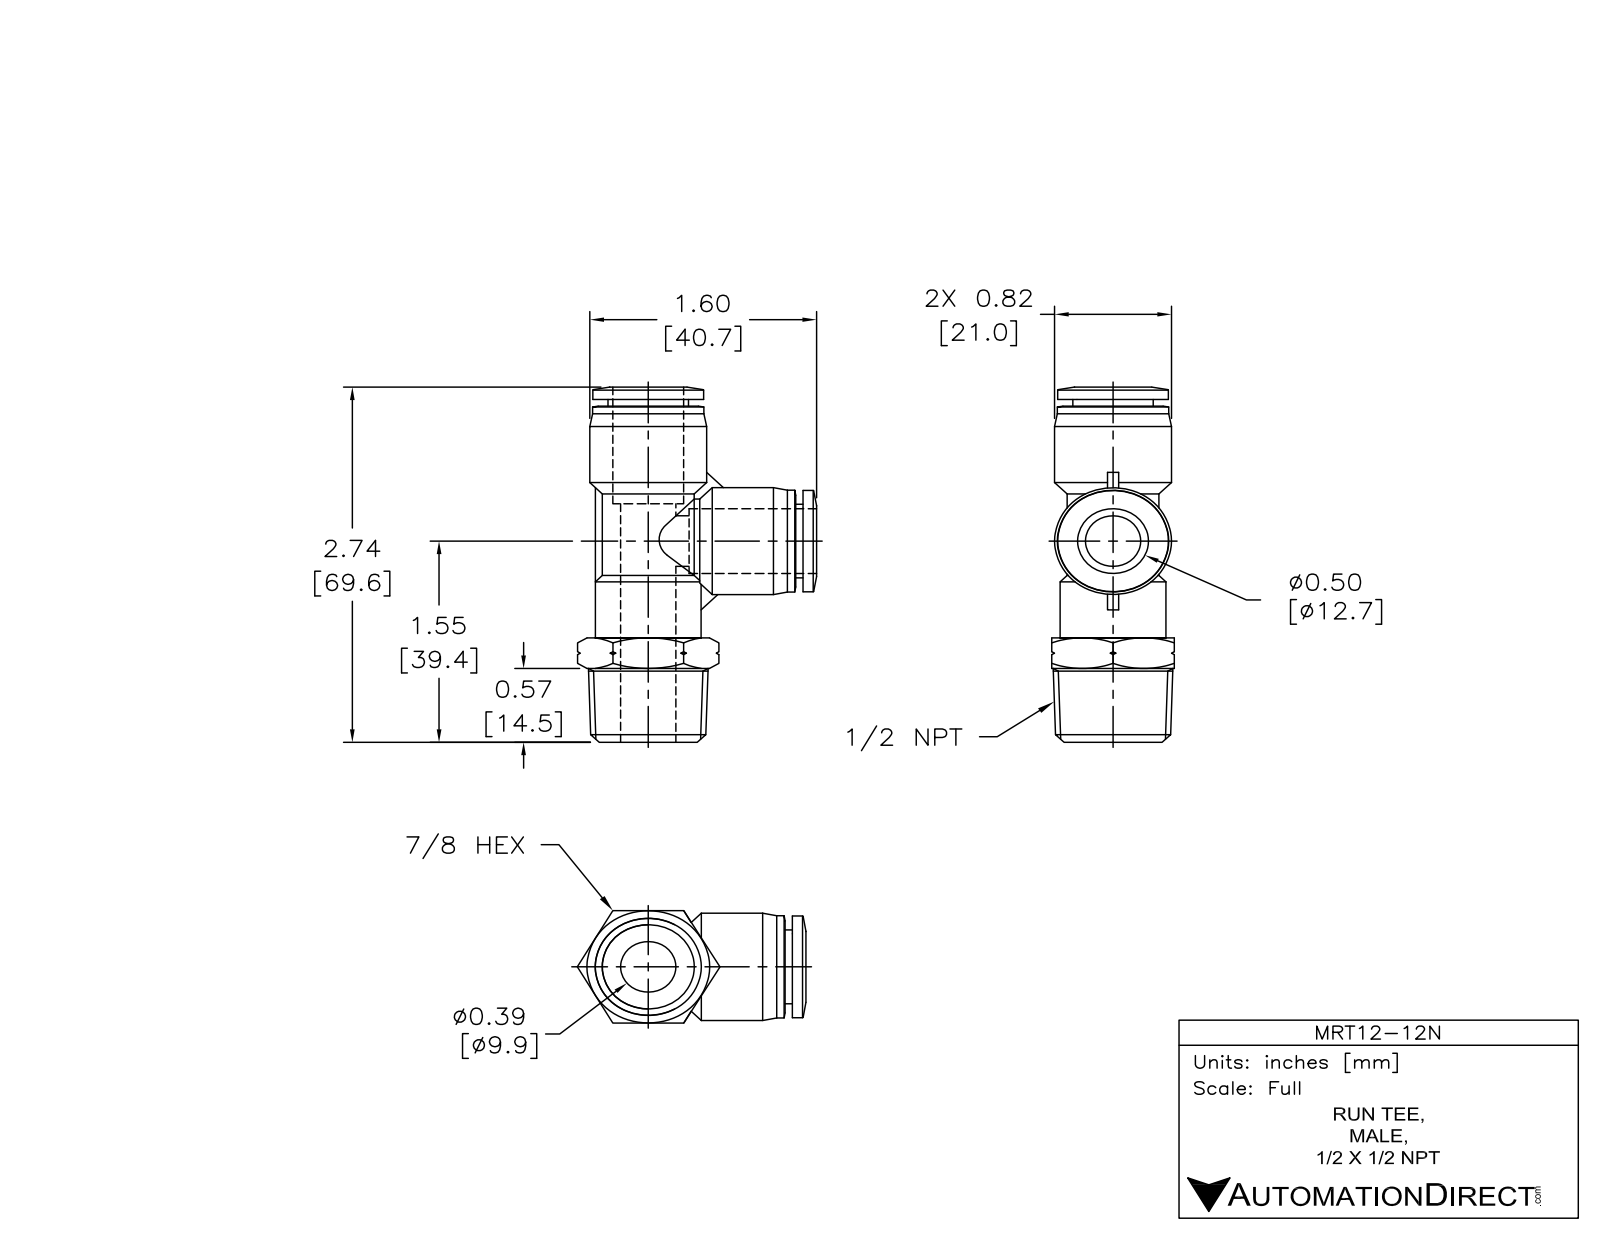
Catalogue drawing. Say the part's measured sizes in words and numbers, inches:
The part is named "MRT12-12N". Its 3-D file was written by "SolidWorks 2015 (AUTOMOTIVE_DESIGN)". It is 1 solid with 115 faces: 23 planar, 30 cylindrical and 62 other. Overall it measures 2.746 by 1.691 by 0.866 inches. Its volume is 1.11 cubic inches and its surface area 16.14 square inches. Round holes: 2 of diameter 0.394, 2 of diameter 0.51. Round bosses or shafts: 2 of diameter 0.827, 2 of diameter 0.787, 2 of diameter 0.783, 2 of diameter 0.65, 2 of diameter 0.569, 1 of diameter 0.748. The main face-to-face distances are 0.866, 0.051, 2.65, 0.762, 0.813, 0.807, 1.843, 2.598, 1.791, 0.394.
